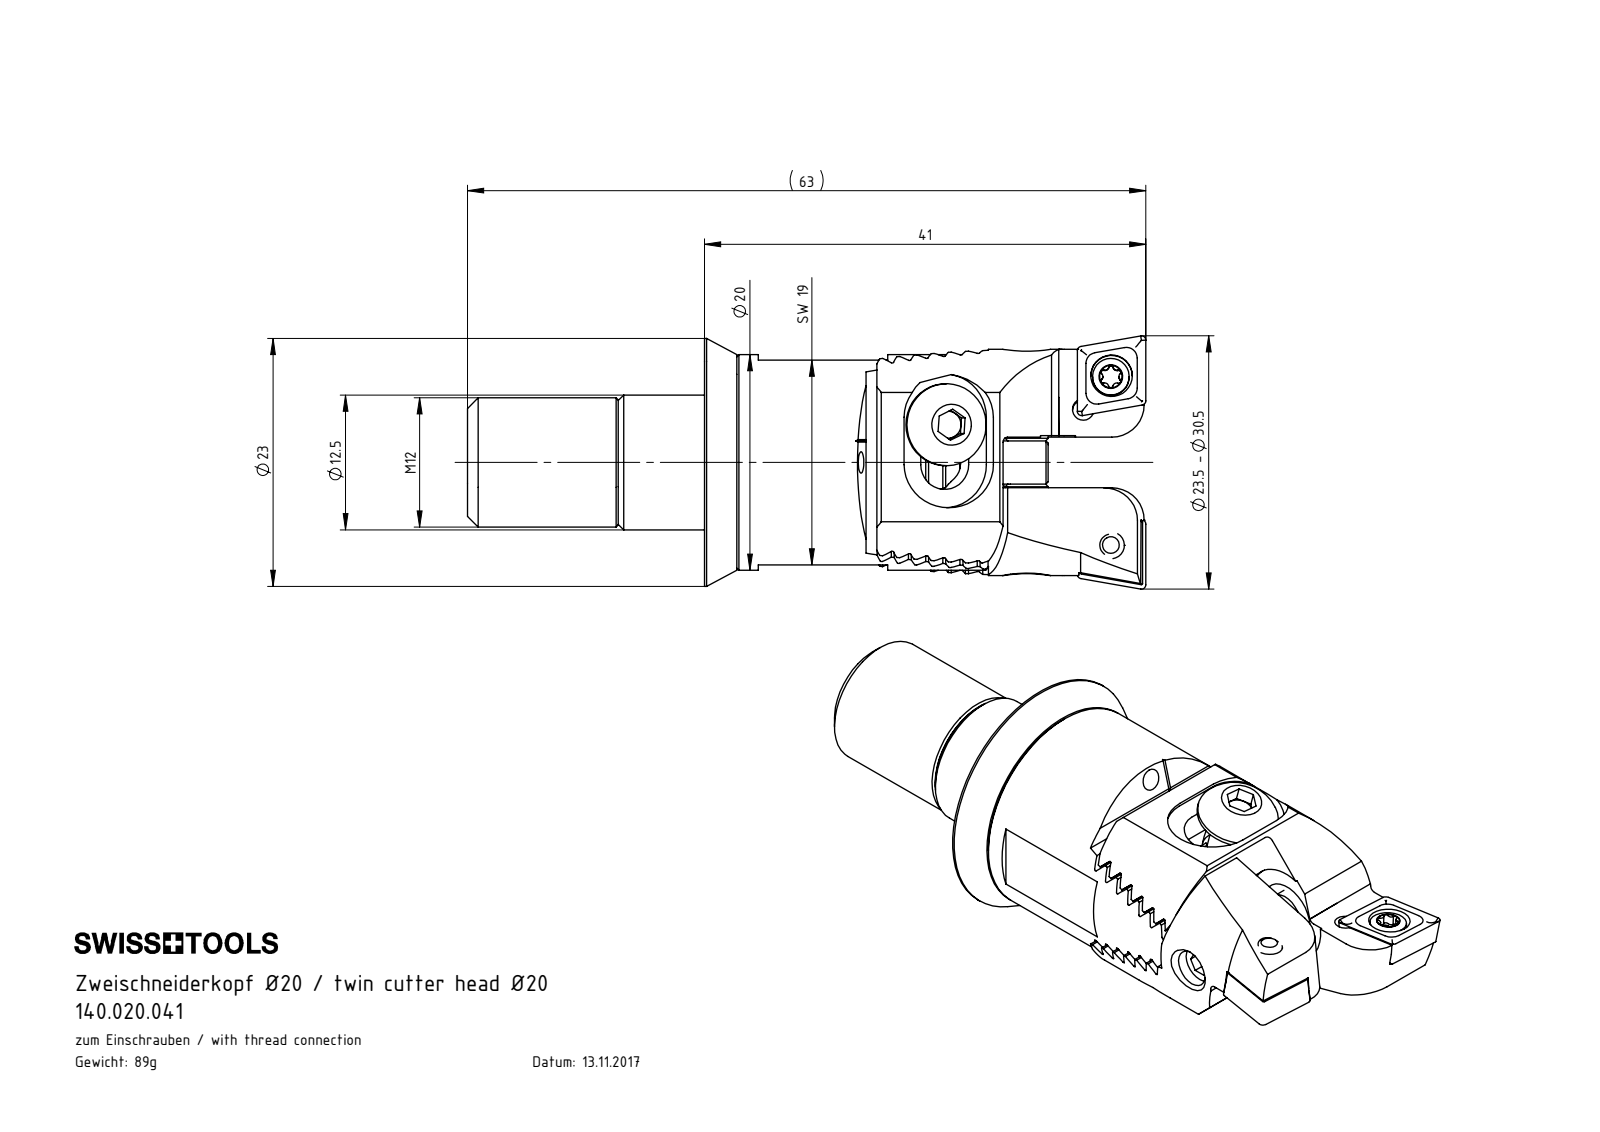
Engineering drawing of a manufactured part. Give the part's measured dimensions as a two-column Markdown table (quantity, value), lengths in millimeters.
| quantity | value |
| --- | --- |
| part name | Z20-WCA.001.015; D23-D20.HP4.003_A; Z20-ER3.001.007_A; CCMT060204 (+7 more) |
| STEP written by | SolidWorks 2017 (CONFIG_CONTROL_DESIGN) |
| units | millimeters |
| bodies | 14 solids, 764 faces (340 planar, 227 cylindrical, 197 other) |
| overall size | 62.96 × 23.5 × 23 |
| volume | 11 454 mm³ |
| surface area | 9 433 mm² |
| round holes (diameter × count) | 2 × 6, 3.3 × 3, 1 × 2, 2.05 × 2, 2.8 × 2, 3.85 × 2, 5 × 2, 2.5 × 1, 3.5 × 1, 6.8 × 1, 8.5 × 1, 9.1 × 1 |
| round bosses / shafts (diameter × count) | 4 × 4, 7.6 × 2, 3.4 × 2, 2.5 × 2, 23 × 1, 20 × 1, 12 × 1, 8 × 1 |
| partial cylindrical surfaces (radius × count) | 0.12 × 26, 0.21 × 12, 0.36 × 10, 1 × 8, 0.5 × 4, 2.3 × 4, 4 × 4, 0.36 × 2 |
| main face-to-face distances | 1.43, 2.86, 3, 5.71, 4.29, 4.28, 7.14, 2.85, 2.57, 7.15 |
| hole center spacings | 3.99, 4.09, 6, 13.08, 13.17, 15.96, 9.77, 11.6 |
